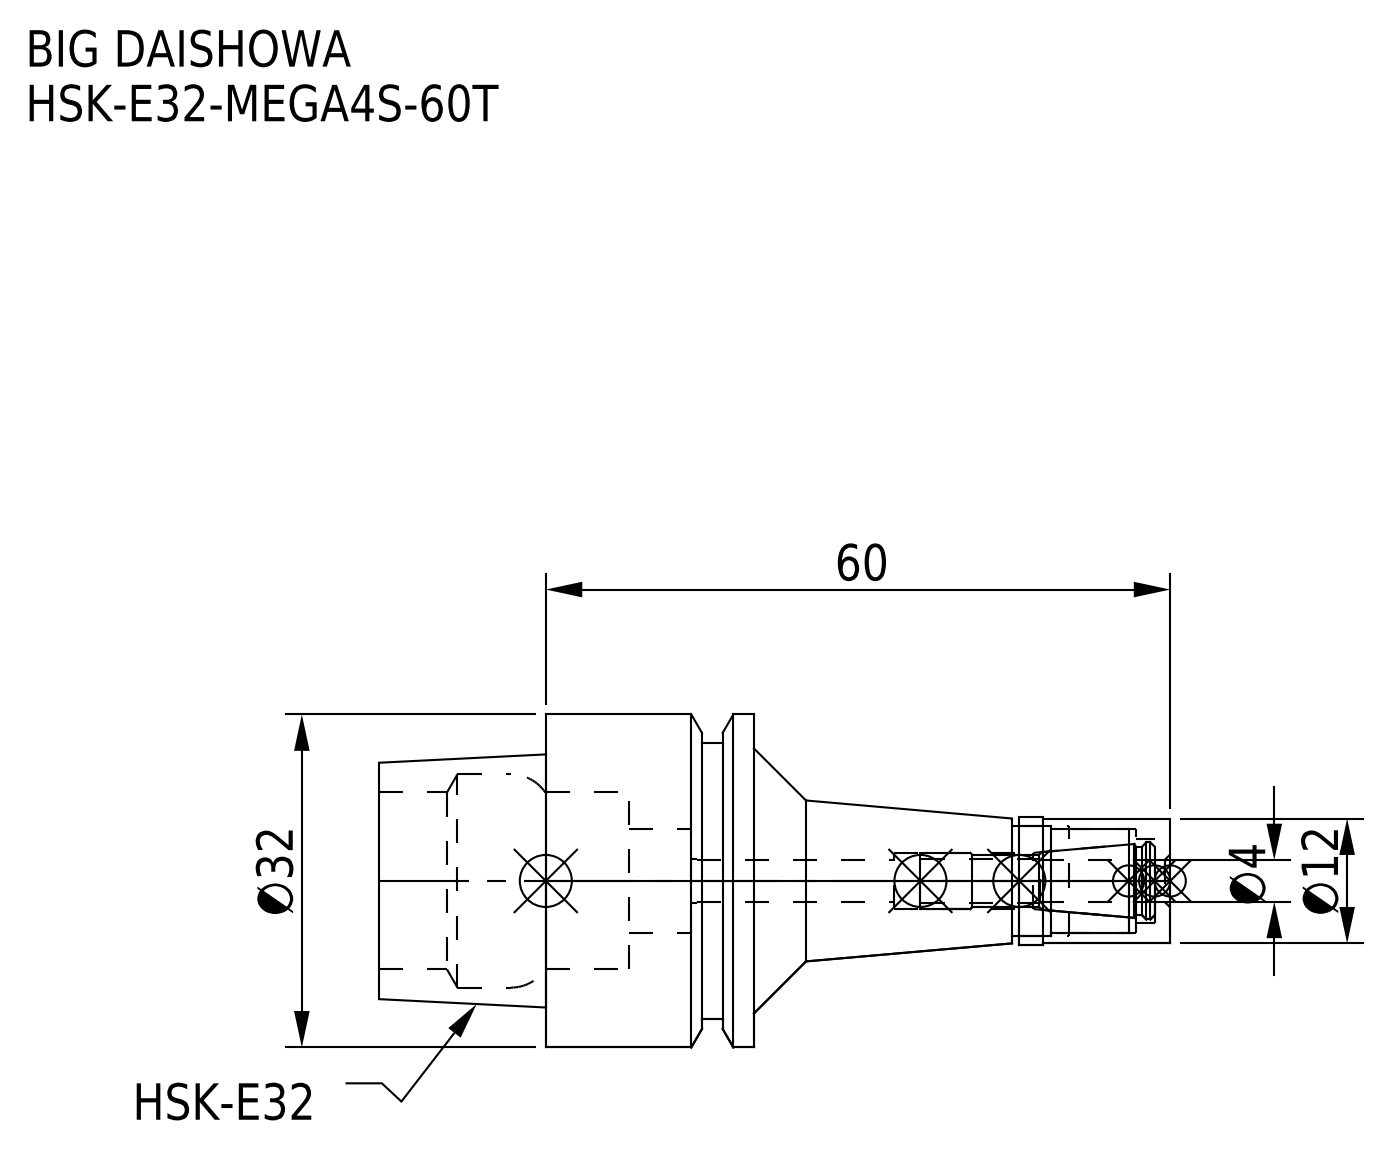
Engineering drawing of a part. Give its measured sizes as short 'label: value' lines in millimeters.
name: DXF_TEMP_ASSY_ASM_4_ASM.stp; HSK-E32-MEGA4S-60T-040-FreeParts; HSK-E32-MEGA4S-60T-040.stp; MGN4S_1.stp (+3 more)
written by: SolidWorks 2019 (CONFIG_CONTROL_DESIGN)
unit: mm
bodies: 2 solids, 74 faces (18 planar, 38 cylindrical, 18 other)
size: 76 × 32 × 32
volume: 20 953 mm³; area: 9 779 mm²
holes: 1× ⌀4.1, 1× ⌀4.2, 1× ⌀5.4, 1× ⌀8, 1× ⌀10, 1× ⌀10.5, 1× ⌀17, 1× ⌀20.5
bosses: 1× ⌀32, 1× ⌀26.5, 1× ⌀12.3, 1× ⌀12
face distances: 20, 36, 16, 12.05, 7.95, 23.95, 3, 15, 40, 52.05
